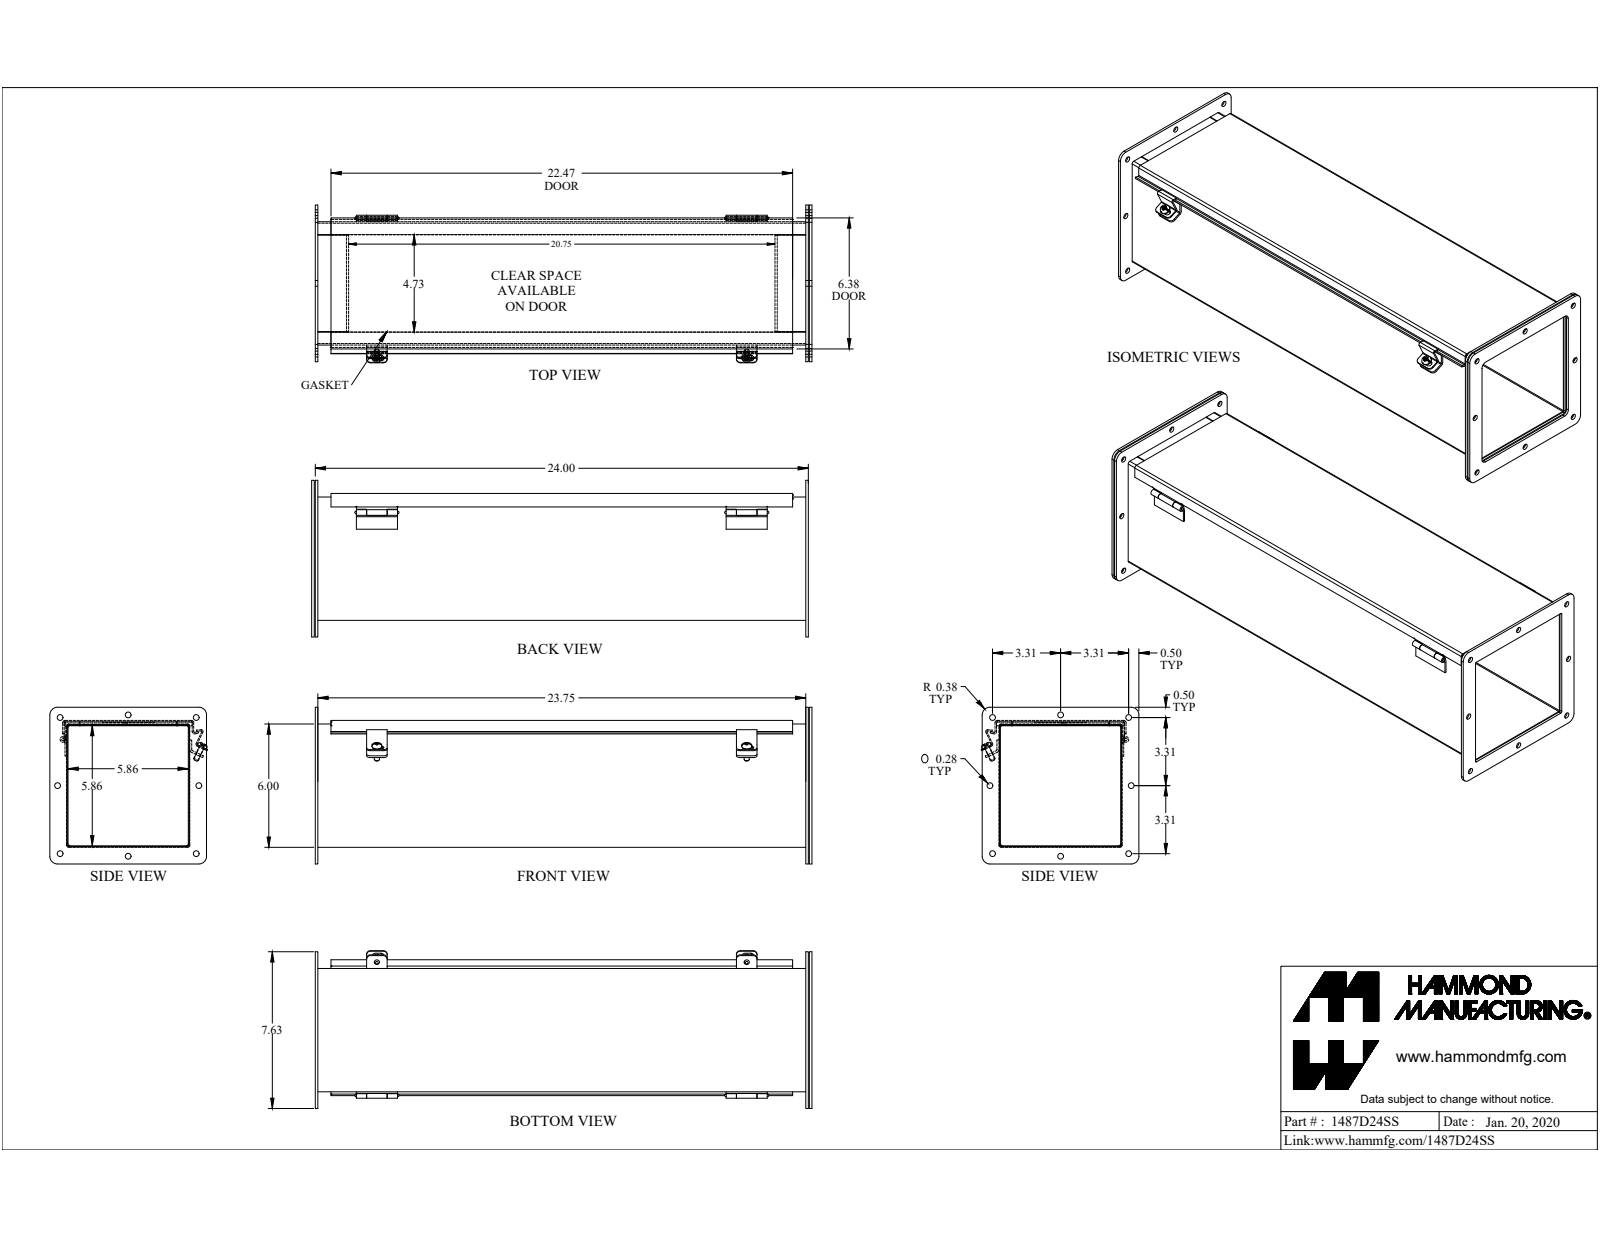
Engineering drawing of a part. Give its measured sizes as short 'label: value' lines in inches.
name: 1487D24SS
written by: SolidWorks 2019 (CONFIG_CONTROL_DESIGN)
unit: in
bodies: 27 solids, 554 faces (350 planar, 152 cylindrical, 52 other)
size: 24.546 × 7.677 × 7.625
volume: 63.29 in³; area: 1 599 in²
holes: 8× ⌀0.281, 2× ⌀0.213, 1× ⌀0.187, 1× ⌀0.196, 1× ⌀0.258, 1× ⌀0.35
bosses: 3× ⌀0.25, 2× ⌀0.48, 1× ⌀0.5, 1× ⌀0.337, 1× ⌀0.18
rounds: 8× R0.188, 8× R0.375, 7× R0.036, 7× R0.108, 6× R0.02, 4× R0.03, 4× R0.063, 4× R0.141
face distances: 0.072, 5.928, 6.1, 6, 5.856, 6.172, 6.028, 0.172, 0.187, 0.125
hole spacings: 7.519, 3.315, 3.315, 4.861, 4.861, 6.625, 6.625, 9.369
